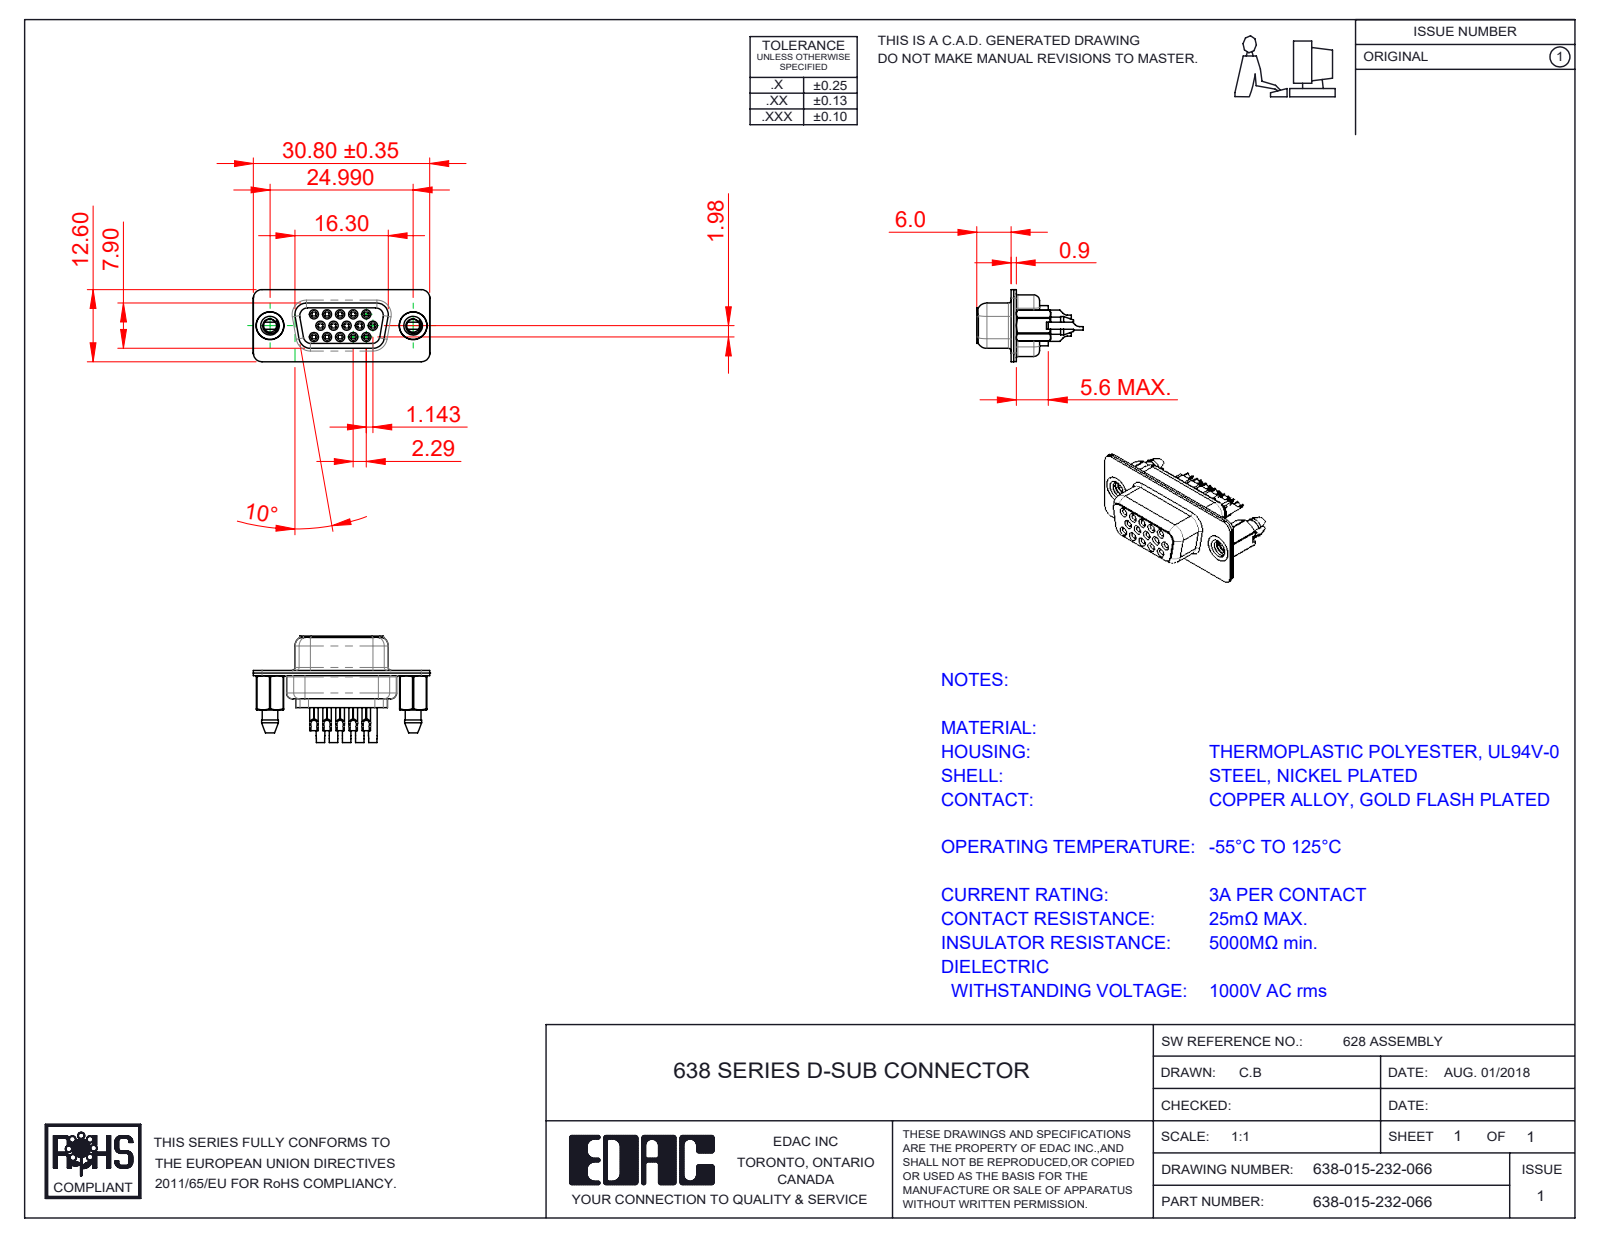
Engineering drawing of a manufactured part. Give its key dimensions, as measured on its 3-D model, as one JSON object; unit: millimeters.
{"part_name": "638 Shell Rear_15 Contacts; 638-015-232-066; 638 Contact Row 1_32; 638 4-40 Threaded Boardlock_LP (+4 more)", "step_written_by": "SolidWorks 2020 (CONFIG_CONTROL_DESIGN)", "units": "millimeters", "bodies": {"solids": 20, "faces": 1688, "planar": 414, "cylindrical": 544, "other": 730}, "overall_size": [30.81, 18.6, 12.6], "volume_mm3": 1716, "surface_area_mm2": 6146, "round_holes": [[0.8, 15], [1, 15], [1.1, 15], [1.6, 15], [1.7, 15], [1.8, 15], [2, 2], [2.26, 2], [4, 2], [4.05, 2], [4.85, 2]], "round_bosses_or_shafts": [[2, 15], [1.5, 15], [1.2, 15], [4.95, 2], [4.8, 2]], "partial_cylinders_radius": [[1.5, 22], [2, 12], [0.28, 10], [1.55, 8], [1, 7], [1.35, 5], [0.25, 4], [0.5, 4]], "face_to_face_distances": [0.45, 0.9, 0.4, 1.43, 8.88, 6.6, 1.4, 6, 2.28, 4.76], "hole_center_spacings": [3.96, 2.28, 4.57, 2.29, 6.05, 6.04, 6.86, 7.92]}
